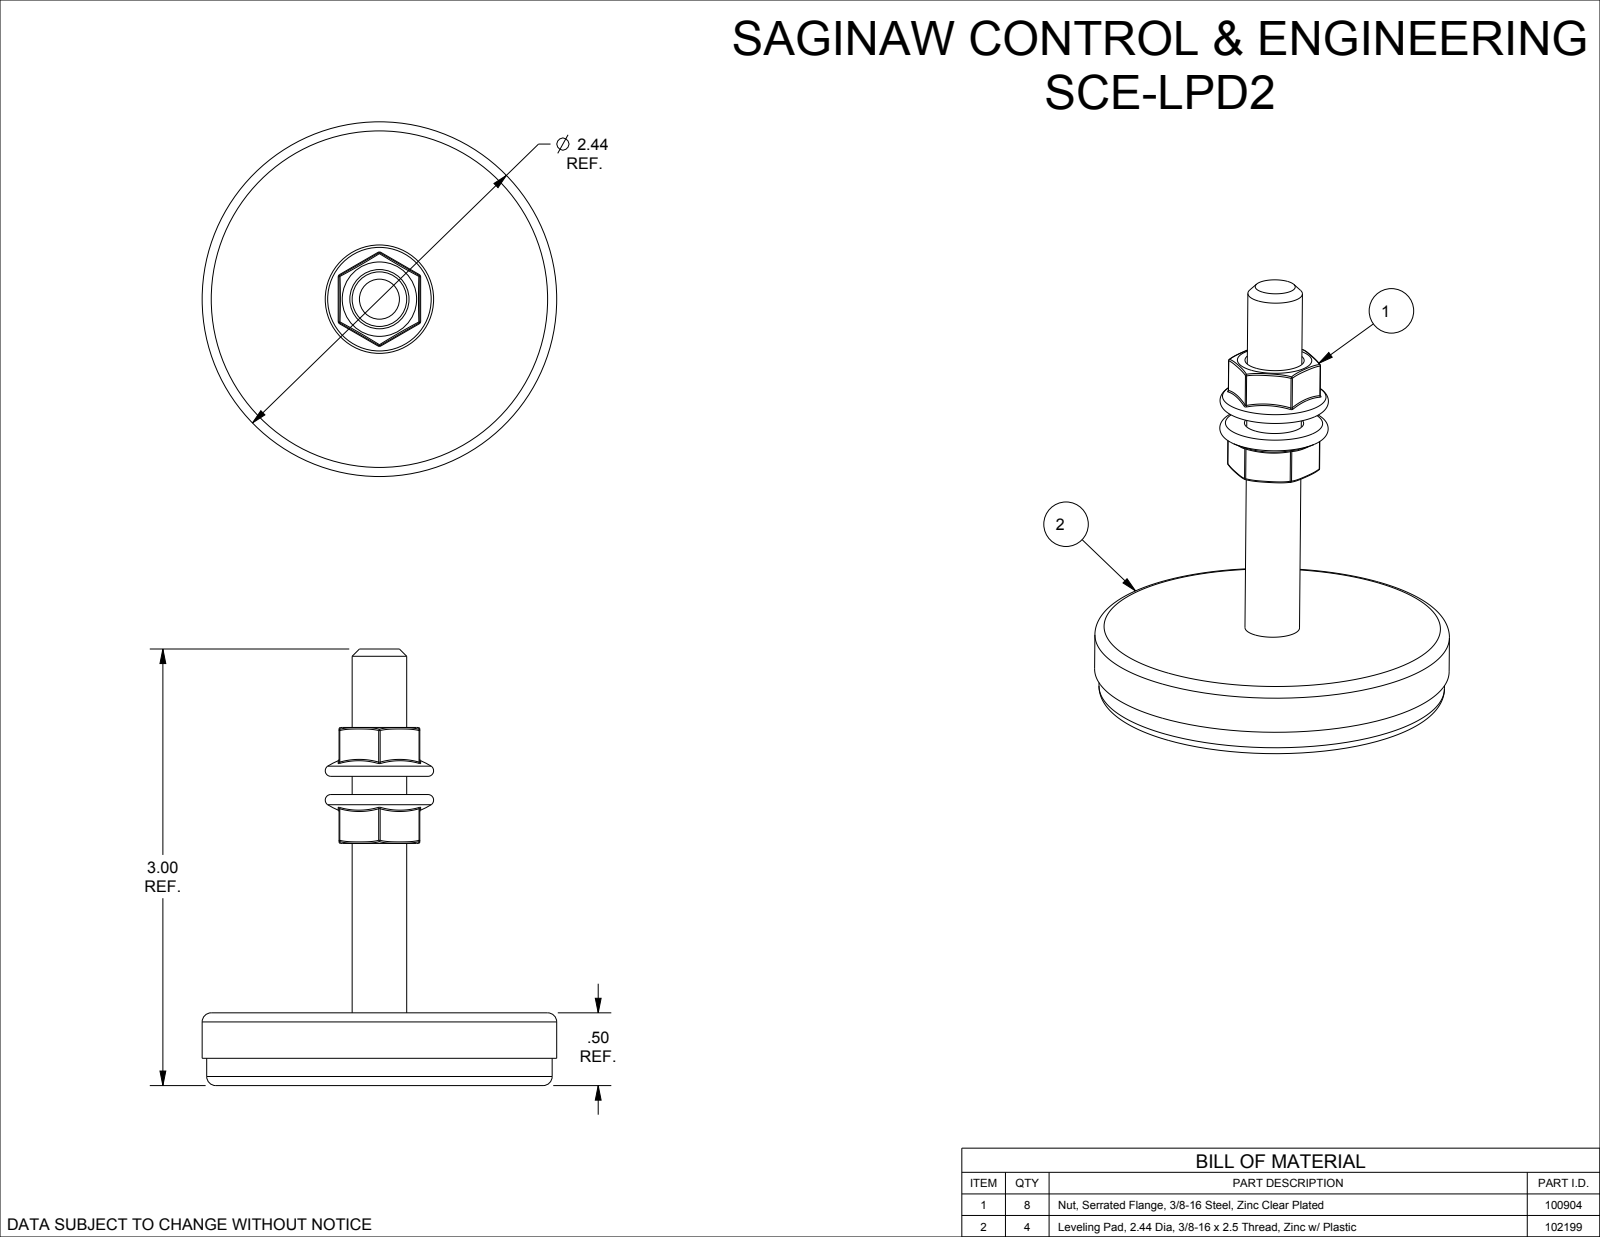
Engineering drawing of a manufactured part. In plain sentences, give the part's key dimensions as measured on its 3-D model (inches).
The part is named "SCE-LPD2". Its 3-D file was written by "SolidWorks 2019 (CONFIG_CONTROL_DESIGN)". It is 12 solids with 400 faces: 84 planar, 72 cylindrical and 244 other. Overall it measures 7.438 by 7.438 by 3 inches. Its volume is 10.62 cubic inches and its surface area 76.03 square inches. Round holes: 4 of diameter 0.367, 4 of diameter 0.437. Round bosses or shafts: 4 of diameter 2.437, 2 of diameter 2.375, 2 of diameter 2.375, 2 of diameter 0.375, 2 of diameter 0.375. Partial cylindrical surfaces (rounded edges, fillets, slot ends): 24 of radius 0.01. The main face-to-face distances are 0.5, 0.555, 0.313, 0.187, 2.5, 4.33, 1.5, 1.813, 2, 0.125. The hole center spacings are 5, 7.071.
